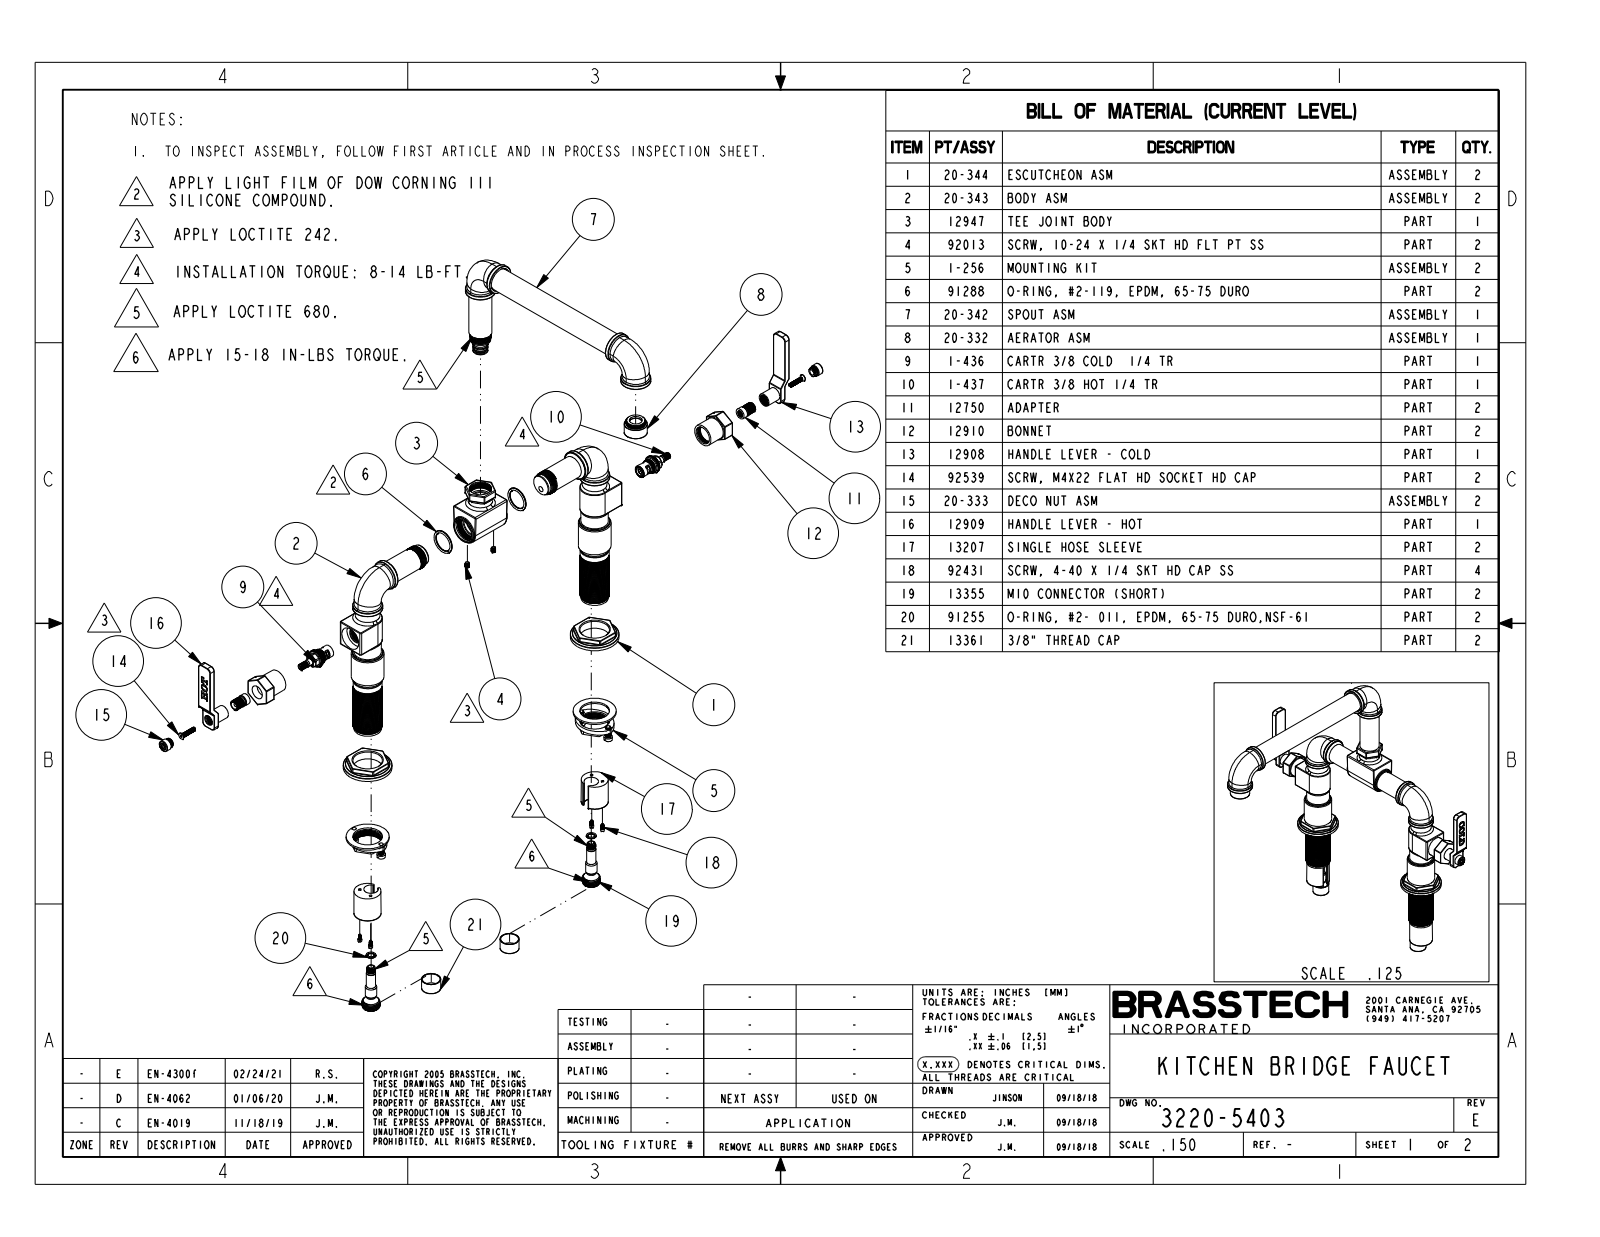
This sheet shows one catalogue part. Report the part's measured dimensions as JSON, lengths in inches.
{"part_name": "3220-5403", "step_written_by": "CREO PARAMETRIC BY PTC INC, 2018400 (AUTOMOTIVE_DESIGN)", "units": "inches", "bodies": {"solids": 2, "faces": 1034, "planar": 227, "cylindrical": 289, "other": 518}, "overall_size": [14.528, 11.858, 11.585], "volume_in3": 47.83, "surface_area_in2": 192.8, "round_holes": [[0.18, 1], [0.622, 1], [0.95, 1]], "round_bosses_or_shafts": [[1.375, 6], [1.25, 3], [1.125, 3], [1.06, 3], [2.23, 2], [1.5, 2], [1.05, 2], [0.625, 1]], "partial_cylinders_radius": [[0.02, 76], [0.01, 40], [0.06, 26], [0.04, 24], [0.03, 14], [0.187, 4], [0.675, 2], [0.687, 1]], "face_to_face_distances": [0.3, 1.05, 0.275, 14.067, 1.35, 13.792, 9.61, 1.2, 1.051, 13.291]}
